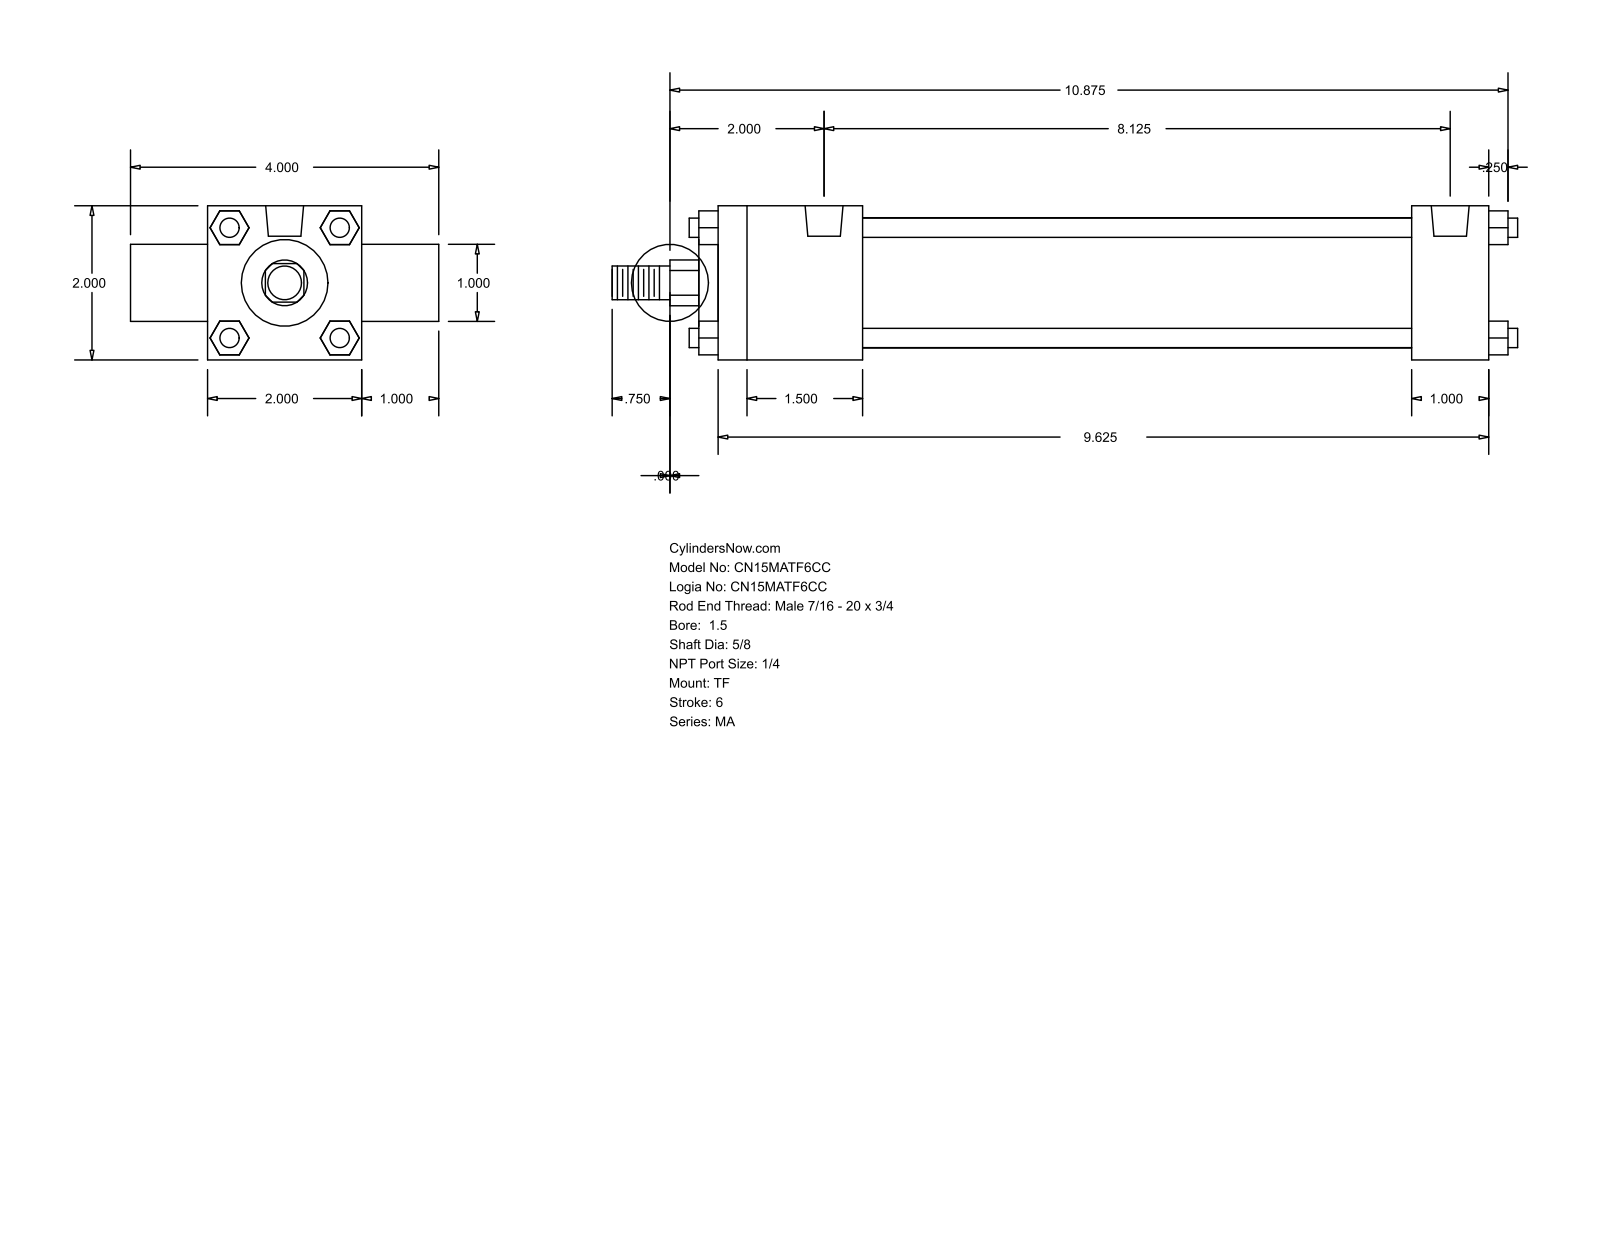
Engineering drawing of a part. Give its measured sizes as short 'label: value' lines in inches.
name: MA_TF__0150_0.625
written by: GSSL Pune (CONFIG_CONTROL_DESIGN)
unit: in
bodies: 0 solids, 120 faces (92 planar, 28 cylindrical, 0 other)
size: 11.75 × 4 × 2
holes: 3× ⌀0.313, 2× ⌀0.492
bosses: 4× ⌀0.25, 1× ⌀1.69, 1× ⌀1.125, 1× ⌀1, 1× ⌀0.625, 1× ⌀0.437
rounds: 1× R0.297
face distances: 2, 10, 1, 0.25, 10.25, 3, 1.875, 9, 7.125, 8.125
hole spacings: 8.125
